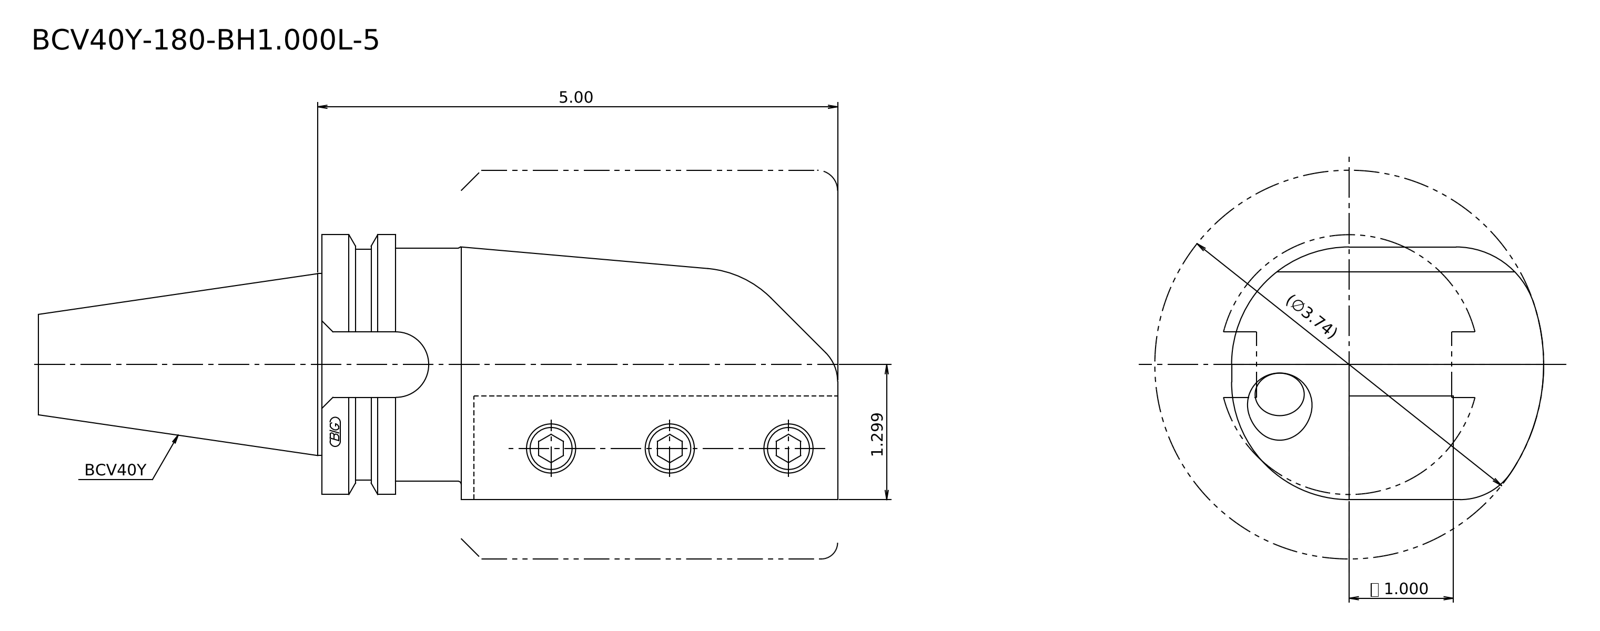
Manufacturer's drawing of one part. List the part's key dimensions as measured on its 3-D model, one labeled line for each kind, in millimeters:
STEP written by: Kubotek KeyCreator 2011 V10.0.2 (22737) (automotive_design)
Units: millimetres
Bodies: 1 solid, 29 faces (15 planar, 10 cylindrical, 4 other)
Overall size (bounding box): 4959.4 × 2013 × 1644.7
Volume: 7 320 000 000 mm³ · Surface area: 30 350 000 mm²
Round bosses / shafts (diameter × count): ⌀1612.9 ×1, ⌀1447.8 ×1, ⌀1431.5 ×1, ⌀1129 ×1
Partial cylindrical surfaces — rounded edges, fillets, slot ends (radius × count): R730.3 ×2, R381 ×1, R508 ×1, R1206.5 ×1
Main face-to-face distances: 645.2, 3200.4, 2336.8, 863.6, 2258.1, 78.7, 942.3, 2741.9, 483.9, 405.1
